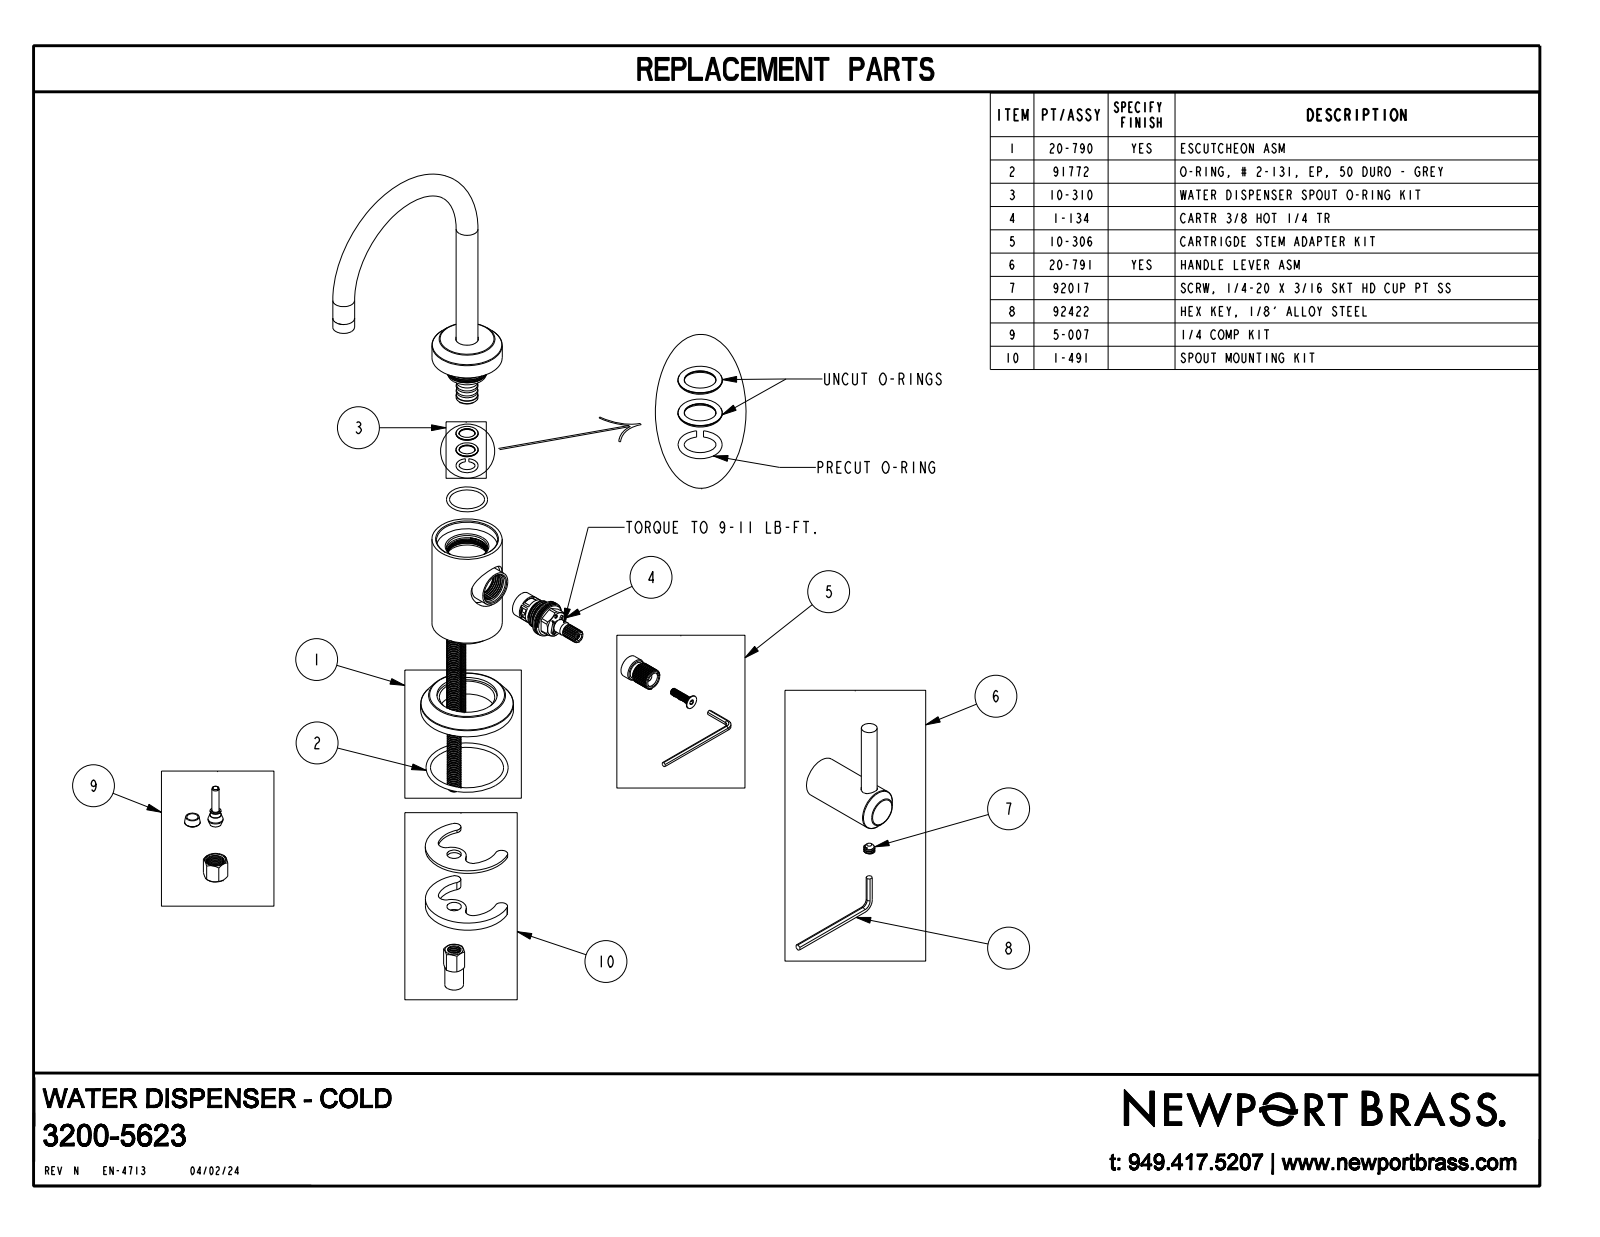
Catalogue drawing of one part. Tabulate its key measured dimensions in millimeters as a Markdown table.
| quantity | value |
| --- | --- |
| part name | 3200-5623 |
| STEP written by | CREO PARAMETRIC BY PTC INC, 2018400 (CONFIG_CONTROL_DESIGN) |
| units | millimeters |
| bodies | 1 solid, 44 faces (8 planar, 16 cylindrical, 20 other) |
| overall size | 234.3 × 135 × 92.7 |
| volume | 172 600 mm³ |
| surface area | 30 610 mm² |
| round holes (diameter × count) | 9.5 × 1, 25.4 × 1 |
| round bosses / shafts (diameter × count) | 12.7 × 2, 54 × 1, 40.9 × 1, 24.1 × 1, 9.1 × 1 |
| main face-to-face distances | 82.7, 10.8, 71.9, 164.4, 153.6, 81.8, 100.1, 89.3, 17.4, 64.3 |
